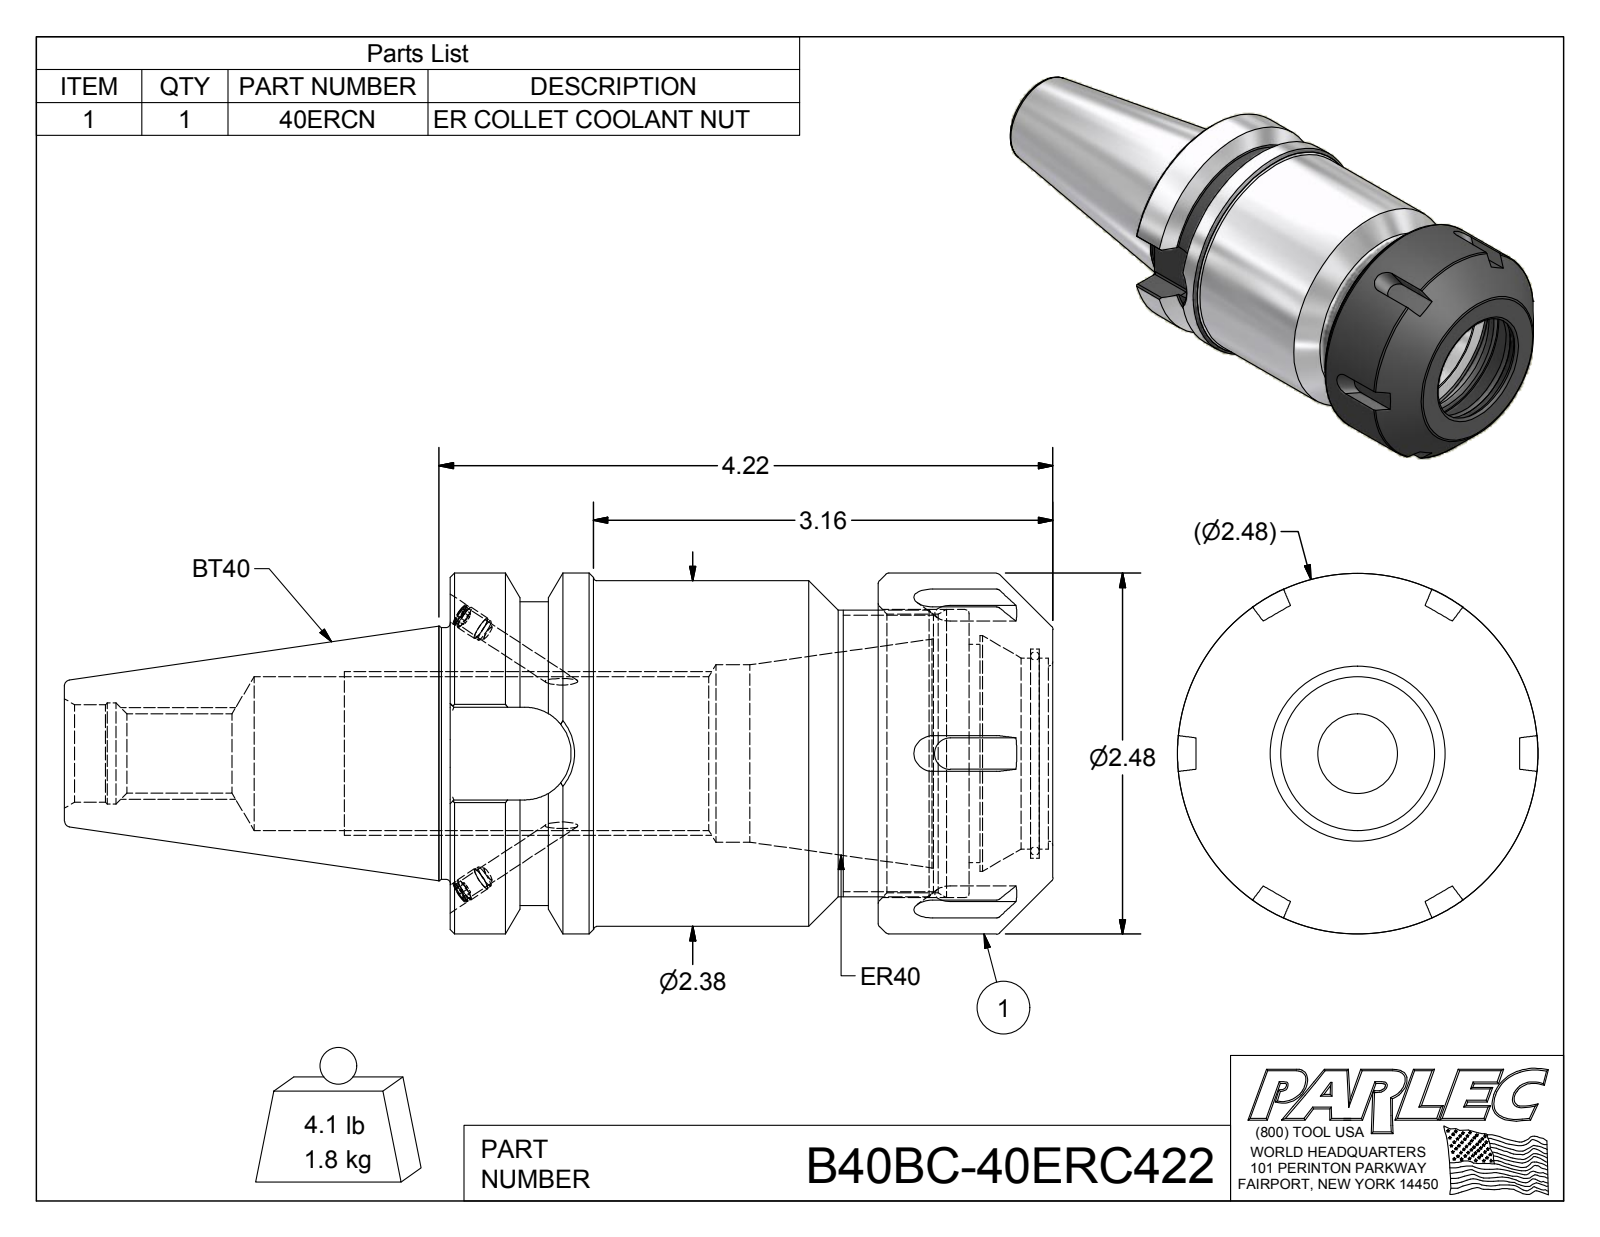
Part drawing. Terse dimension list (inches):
name: B40BC-40ERC422; B40BCB-40ER4-1; 029-965; 40ERCN
written by: Autodesk Inventor 2012 (AUTOMOTIVE_DESIGN)
unit: in
bodies: 4 solids, 167 faces (71 planar, 41 cylindrical, 55 other)
size: 6.795 × 2.48 × 2.48
volume: 14.49 in³; area: 85.85 in²
holes: 2× ⌀0.13, 2× ⌀0.161, 1× ⌀0.545, 1× ⌀0.67, 1× ⌀0.694, 1× ⌀1.057, 1× ⌀1.22, 1× ⌀1.313, 1× ⌀1.437, 1× ⌀1.5, 1× ⌀1.62, 1× ⌀1.916
bosses: 2× ⌀0.165, 2× ⌀0.157, 1× ⌀2.48, 1× ⌀2.48, 1× ⌀2.375, 1× ⌀2.087, 1× ⌀1.969, 1× ⌀1.73
rounds: 8× R0.02, 1× R0.319
face distances: 3.567, 4.142, 0.575, 2.942, 0.625, 1.2, 3.322, 0.38, 0.245, 0.82
